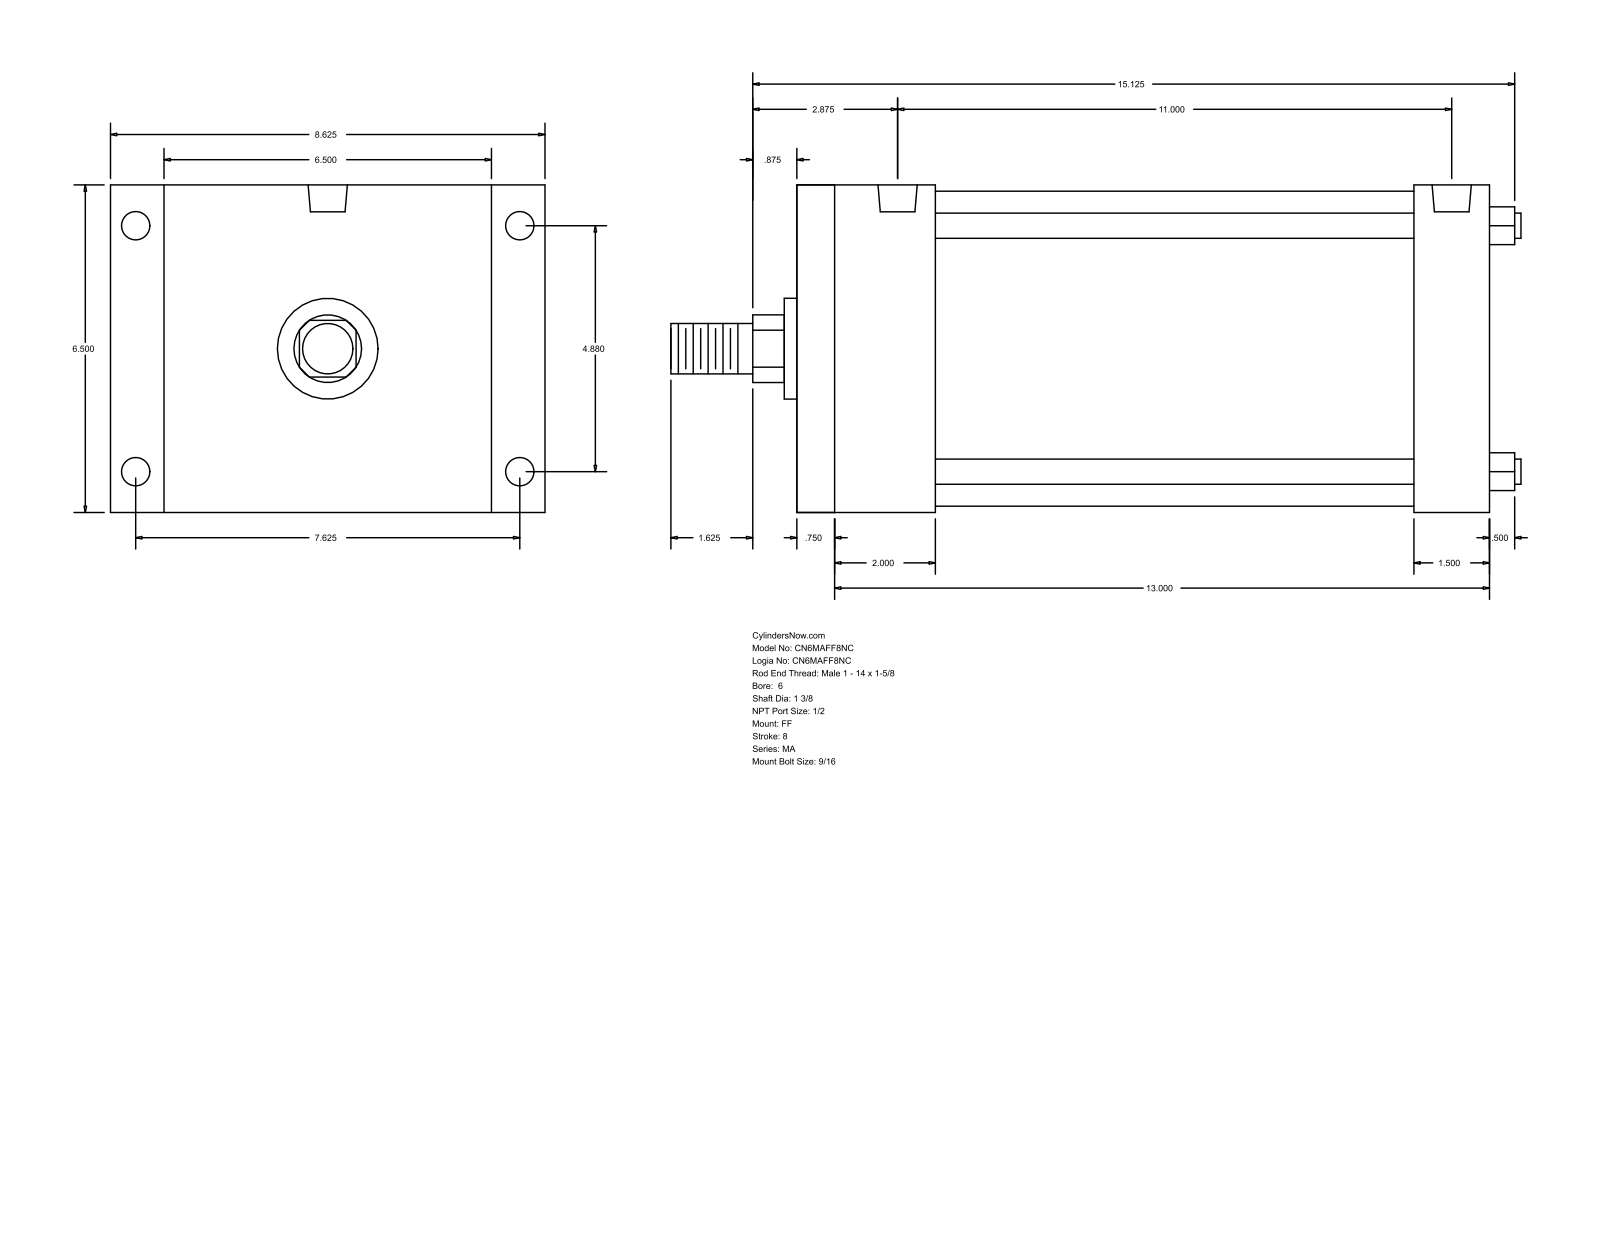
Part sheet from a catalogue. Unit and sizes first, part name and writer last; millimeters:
Units: millimetres
Overall size (bounding box): 428.62 × 219.07 × 165.1
Round holes (diameter × count): ⌀14.29 ×4, ⌀17.46 ×4, ⌀19.77 ×2
Round bosses / shafts (diameter × count): ⌀12.7 ×4, ⌀158.75 ×1, ⌀50.8 ×1, ⌀34.92 ×1, ⌀25.4 ×1
Partial cylindrical surfaces — rounded edges, fillets, slot ends (radius × count): R17.06 ×1
Main face-to-face distances: 165.1, 349.25, 15.87, 333.38, 50.8, 295.28, 38.1, 66.67, 282.58, 311.15
Hole centre spacings: 123.96, 193.68, 229.95, 282.58, 3.18, 279.4
Bodies: 0 solids, 92 faces (64 planar, 28 cylindrical, 0 other)
Part name (STEP PRODUCT): MA_FF__0600_1.375
STEP written by: GSSL Pune (CONFIG_CONTROL_DESIGN)
